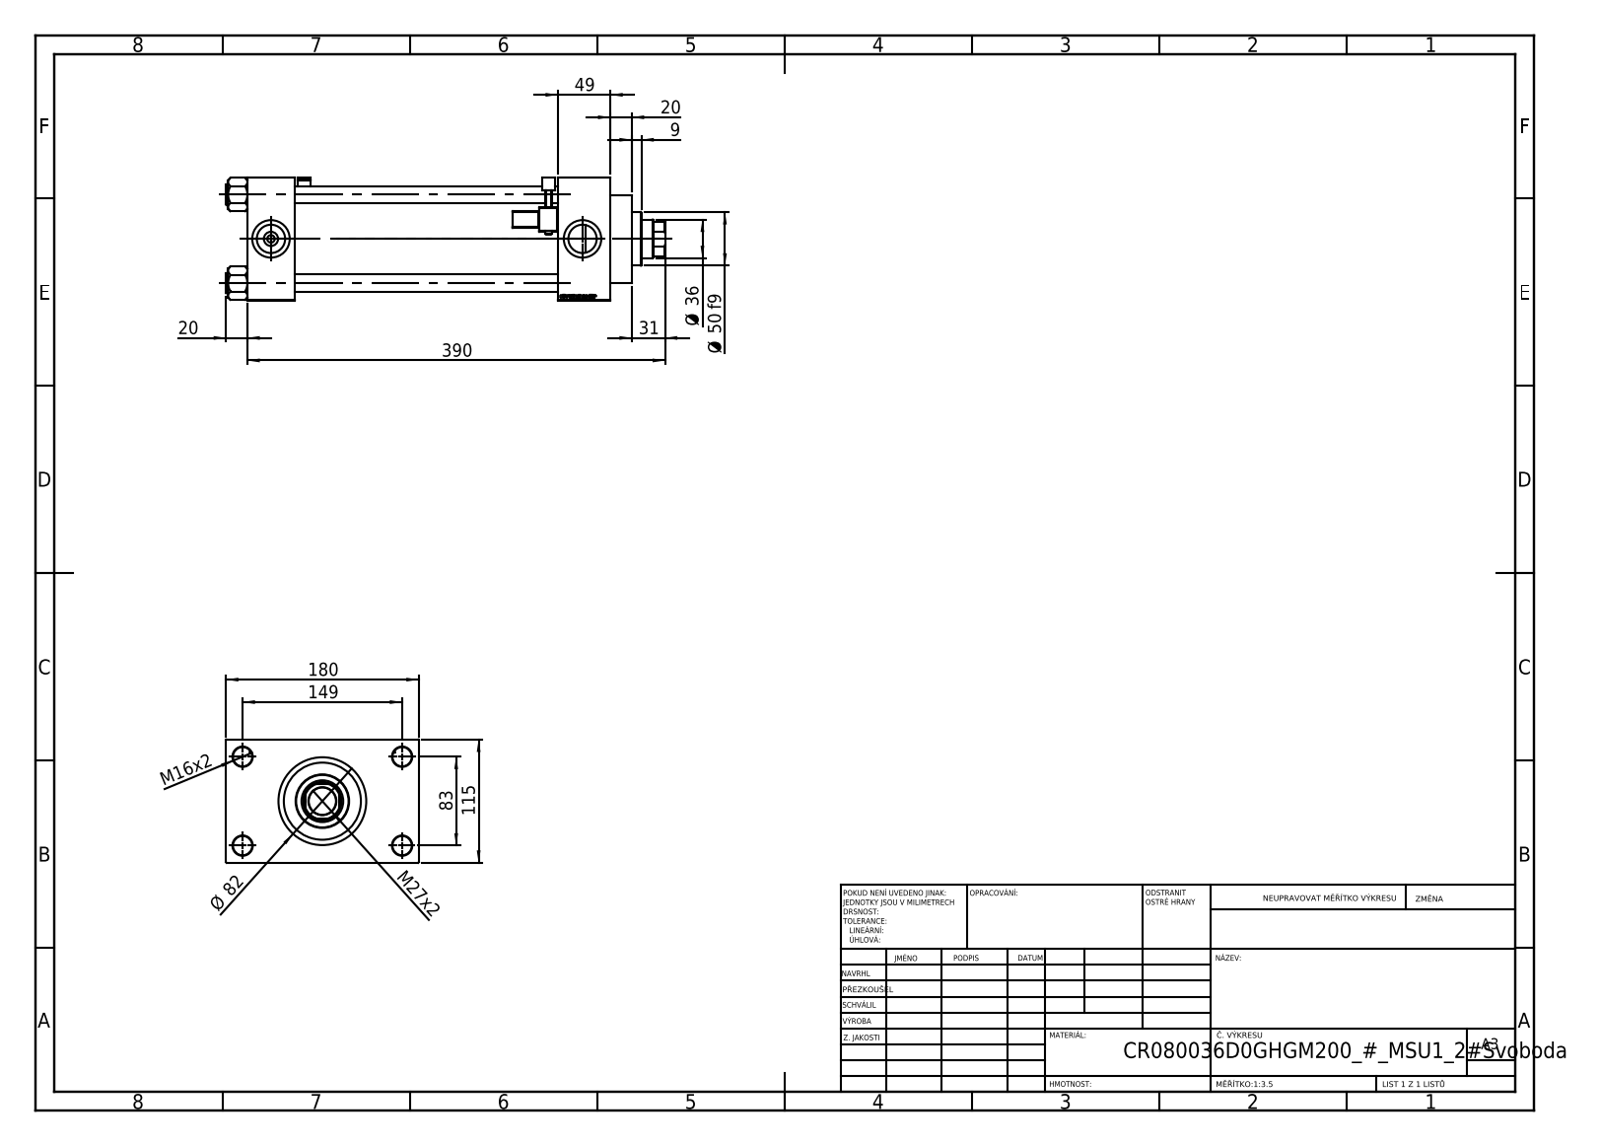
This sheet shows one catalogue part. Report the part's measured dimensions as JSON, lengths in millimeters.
{"part_name": "NUT_M5_D; V215CR_D_TYCINKA; V215_VC_A; V215CR_VCP_D (+2 more)", "step_written_by": "SolidWorks 2019 (CONFIG_CONTROL_DESIGN)", "units": "millimeters", "bodies": {"solids": 13, "faces": 1305, "planar": 603, "cylindrical": 148, "other": 554}, "overall_size": [410, 180, 115], "volume_mm3": 2490000, "surface_area_mm2": 459465, "round_holes": [[16, 4], [18, 4], [7, 2], [26.44, 2], [35, 2], [25.5, 1], [36, 1], [39, 1], [61, 1], [72, 1], [80, 1]], "round_bosses_or_shafts": [[19, 4], [6, 2], [86, 1], [82, 1], [50, 1]], "partial_cylinders_radius": [[0.5, 48], [1, 2], [2.5, 2], [4, 2], [17.5, 1]], "face_to_face_distances": [115, 246, 295, 49, 44, 290, 339, 32.5, 147.5, 180], "hole_center_spacings": [33.15, 58.48, 82.7, 85.28, 89.24, 115.85, 142.43, 83]}
